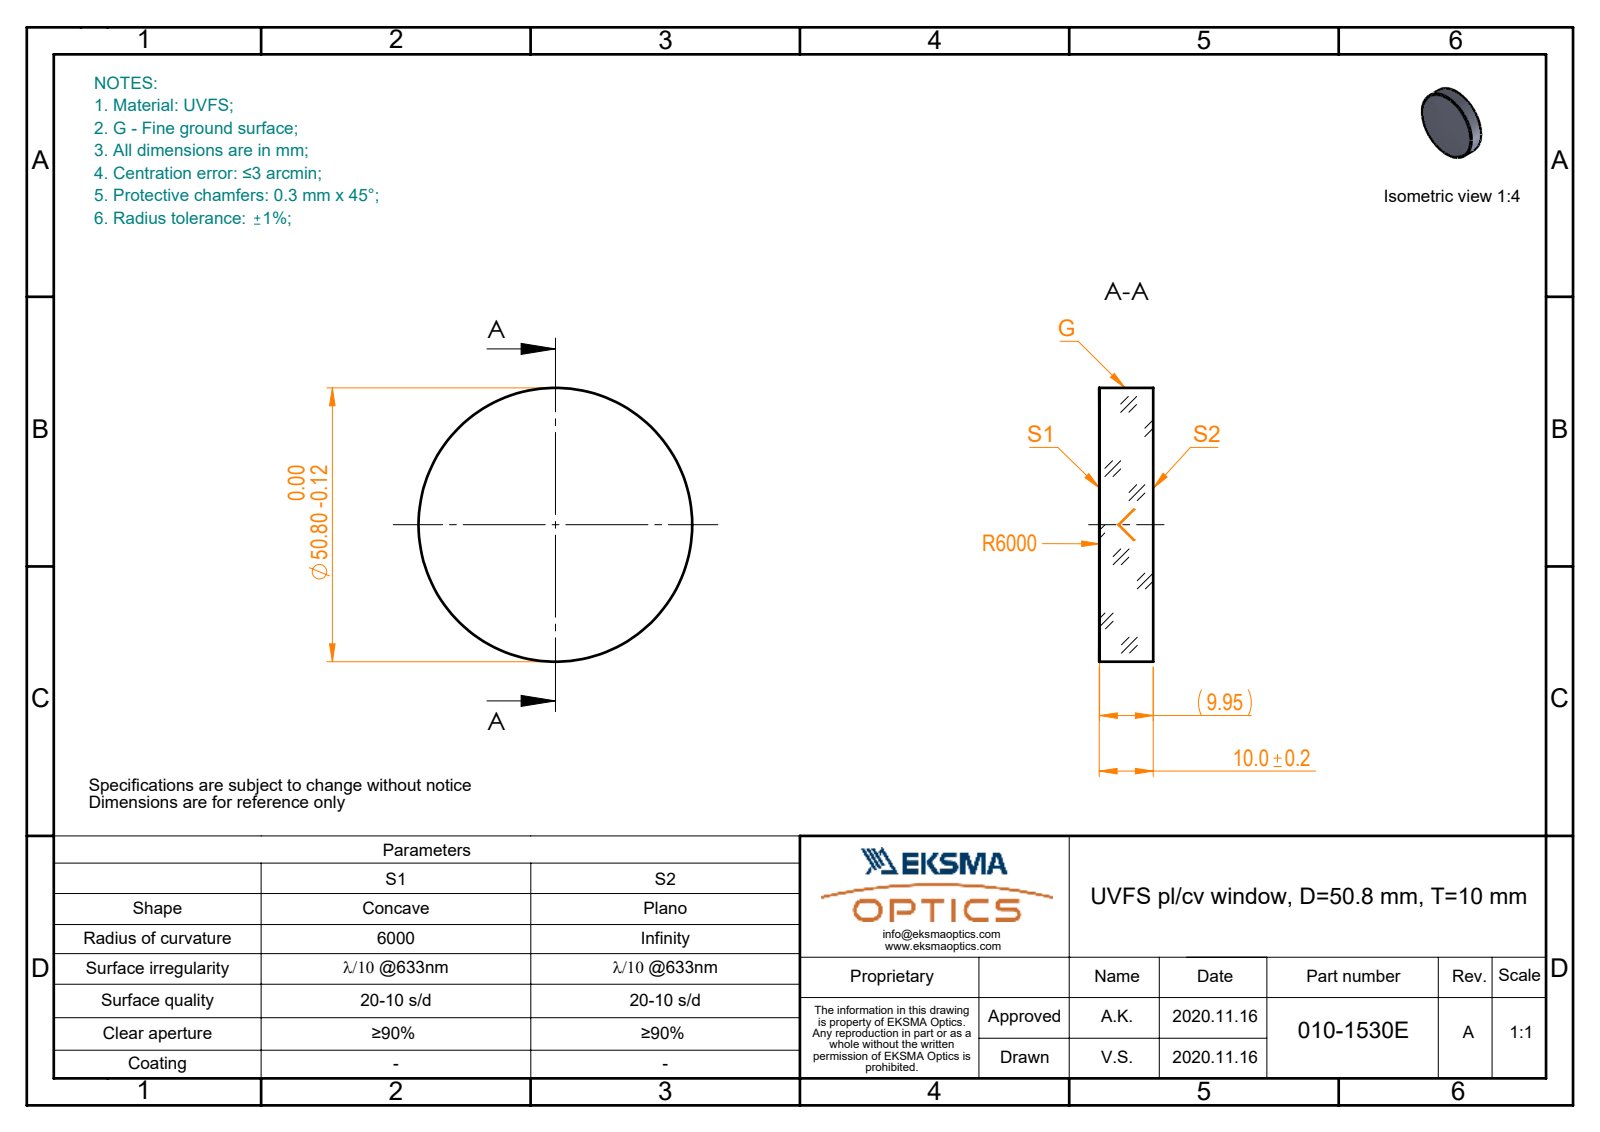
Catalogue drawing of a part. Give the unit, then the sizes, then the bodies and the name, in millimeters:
Units: millimetres
Overall size (bounding box): 50.8 × 50.8 × 10
Round bosses / shafts (diameter × count): ⌀50.8 ×1
Volume: 20 214 mm³ · Surface area: 5 650 mm²
Bodies: 1 solid, 5 faces (1 planar, 2 cylindrical, 2 other)
Part name (STEP PRODUCT): 010-1530E_UVFS_PCV_window
STEP written by: SolidWorks 2019 (CONFIG_CONTROL_DESIGN)
